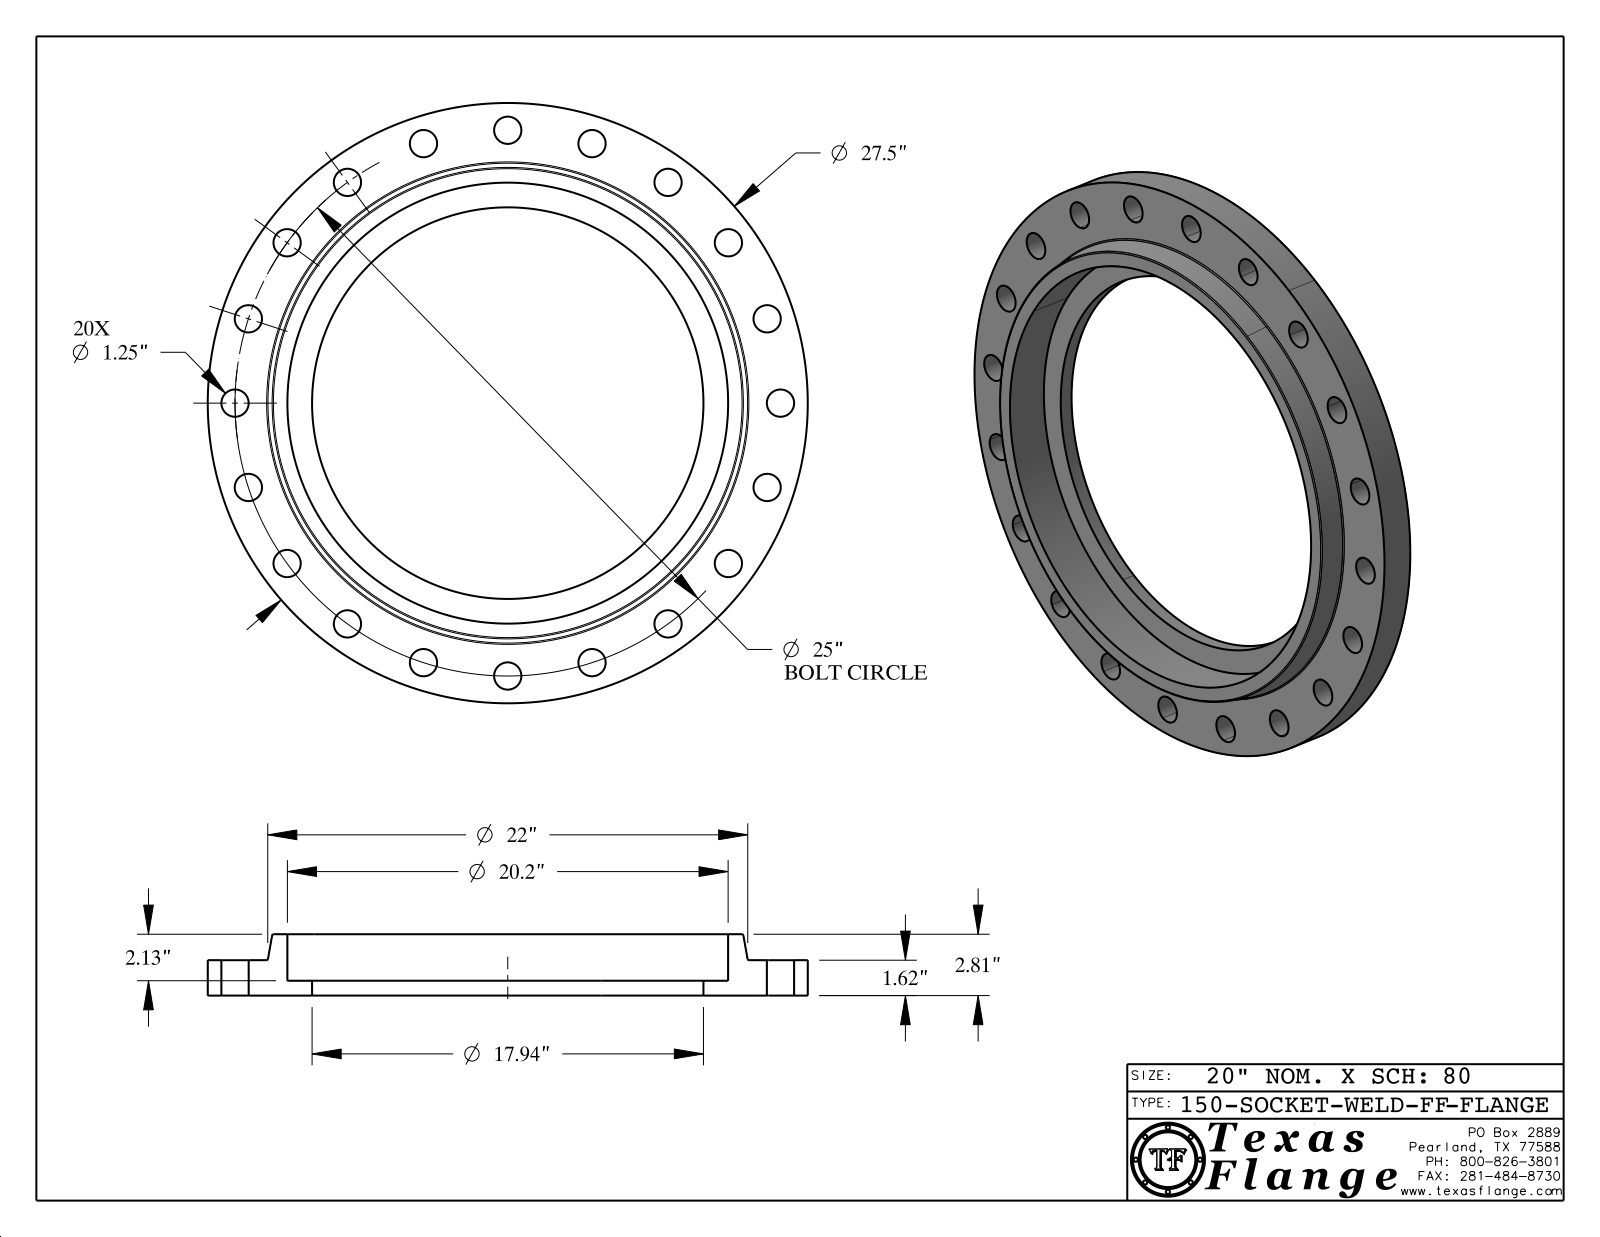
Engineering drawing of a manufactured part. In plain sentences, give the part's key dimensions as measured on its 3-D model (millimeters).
The part is named "150-SOCKET-WELD-FF". Its 3-D file was written by "CATIA V5 STEP AP214 (AUTOMOTIVE_DESIGN)". It is 1 solid with 442 faces: 370 planar, 66 cylindrical and 6 other. Overall it measures 698.5 by 698.5 by 71.4 millimeters. Its volume is 8 387 000 cubic millimeters and its surface area 735 500 square millimeters. Round holes: 20 of diameter 31.8, 1 of diameter 12.6, 1 of diameter 455.6, 1 of diameter 513.1. Round bosses or shafts: 8 of diameter 0.8, 1 of diameter 698.5, 1 of diameter 9.9. The main face-to-face distances are 41.1, 17.3, 23.9, 71.4, 54.1, 30.2, 40.8, 23.5, 0.4, 30.6. The hole center spacings are 317.5, 373.2, 449, 513.7, 603.9, 627.2, 288.3, 565.8.
